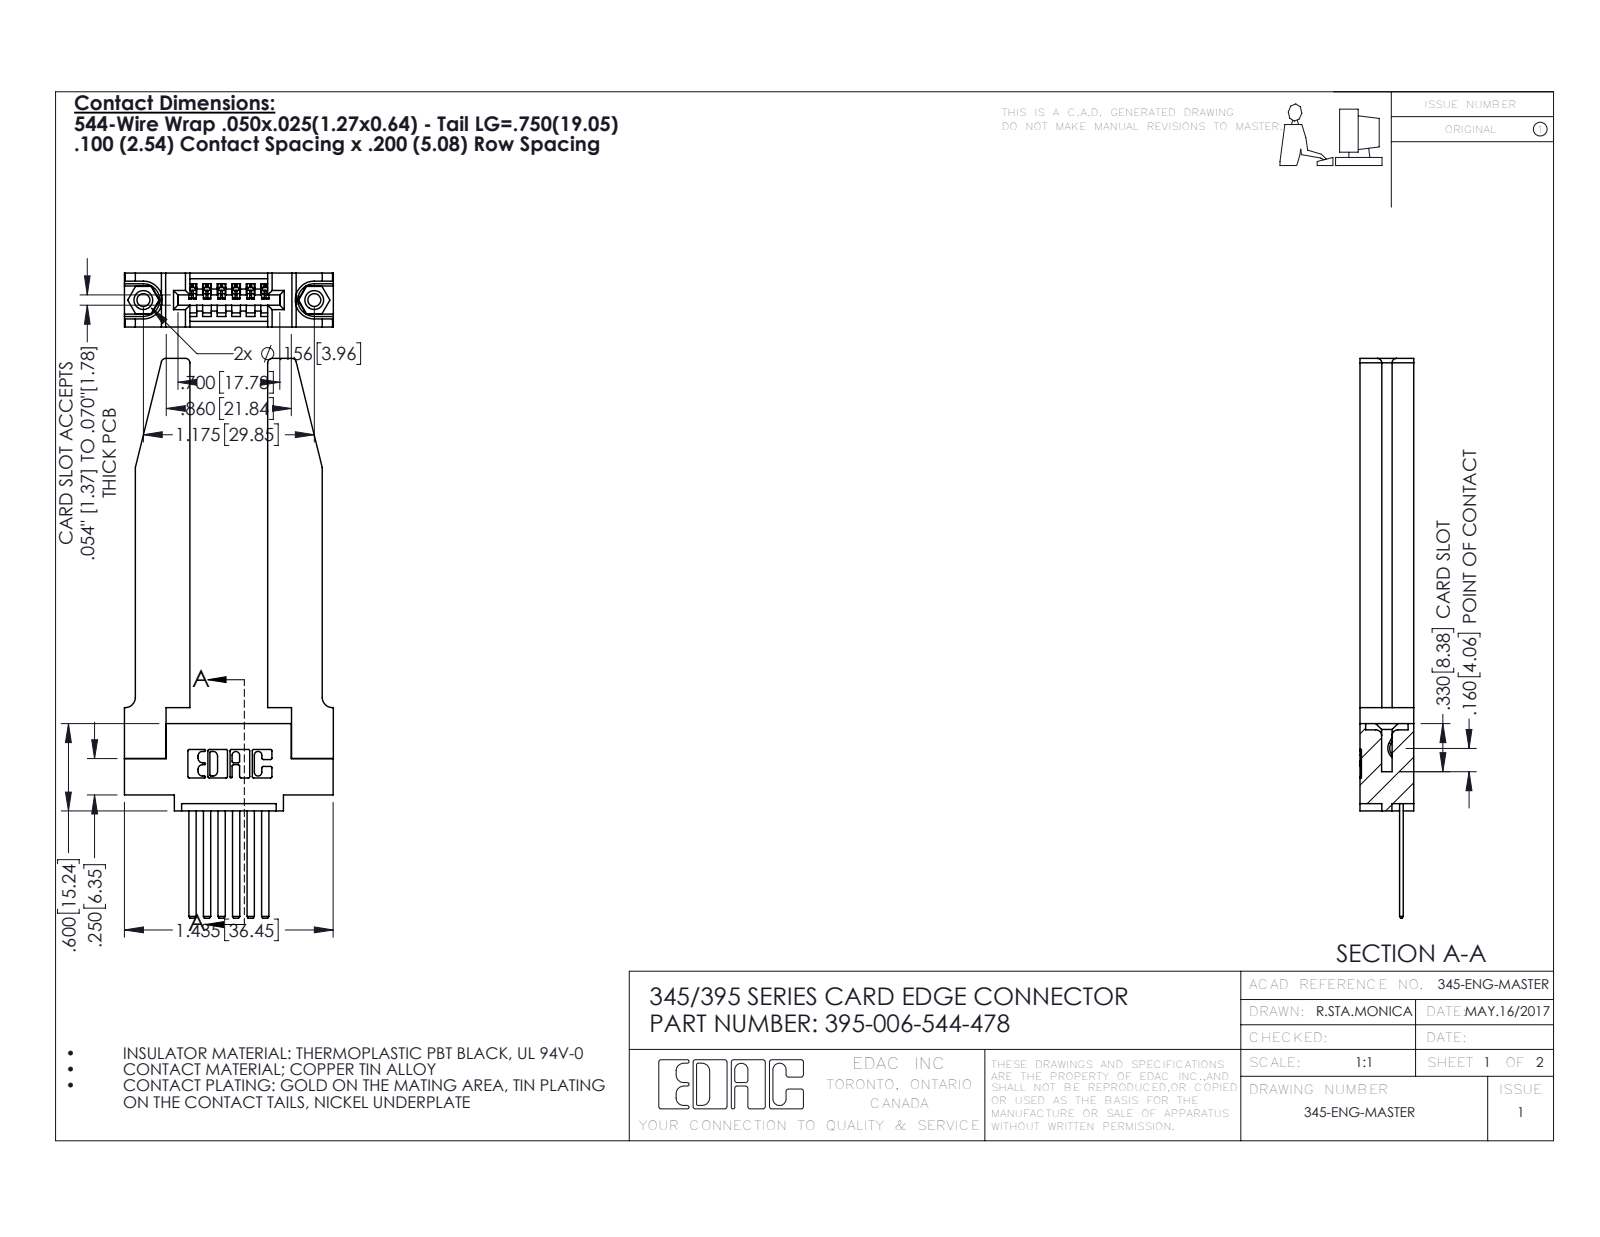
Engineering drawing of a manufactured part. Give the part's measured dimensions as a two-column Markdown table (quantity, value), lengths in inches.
| quantity | value |
| --- | --- |
| part name | 345-220-078_345-220-078; 345-250-001_345-250-001-102; 345 Part_0.110 Offset - 0.156 Dia-TH; 395-006-544-478 (+1 more) |
| STEP written by | SolidWorks 2016 (CONFIG_CONTROL_DESIGN) |
| units | inches |
| bodies | 11 solids, 676 faces (442 planar, 182 cylindrical, 52 other) |
| overall size | 3.847 × 1.436 × 0.37 |
| volume | 0.667 in³ |
| surface area | 16.82 in² |
| round holes (diameter × count) | 0.089 × 2, 0.125 × 2, 0.156 × 2, 0.064 × 1 |
| round bosses / shafts (diameter × count) | 0.155 × 2 |
| partial cylindrical surfaces (radius × count) | 0.01 × 22, 0.006 × 12, 0.03 × 8, 0.007 × 6, 0.031 × 6, 0.026 × 3, 0.031 × 2, 0.04 × 2 |
| main face-to-face distances | 0.37, 0.072, 0.15, 0.298, 0.22, 0.535, 0.148, 0.077, 0.098, 0.272 |
| hole center spacings | 0.27, 0.946, 1.175 |
